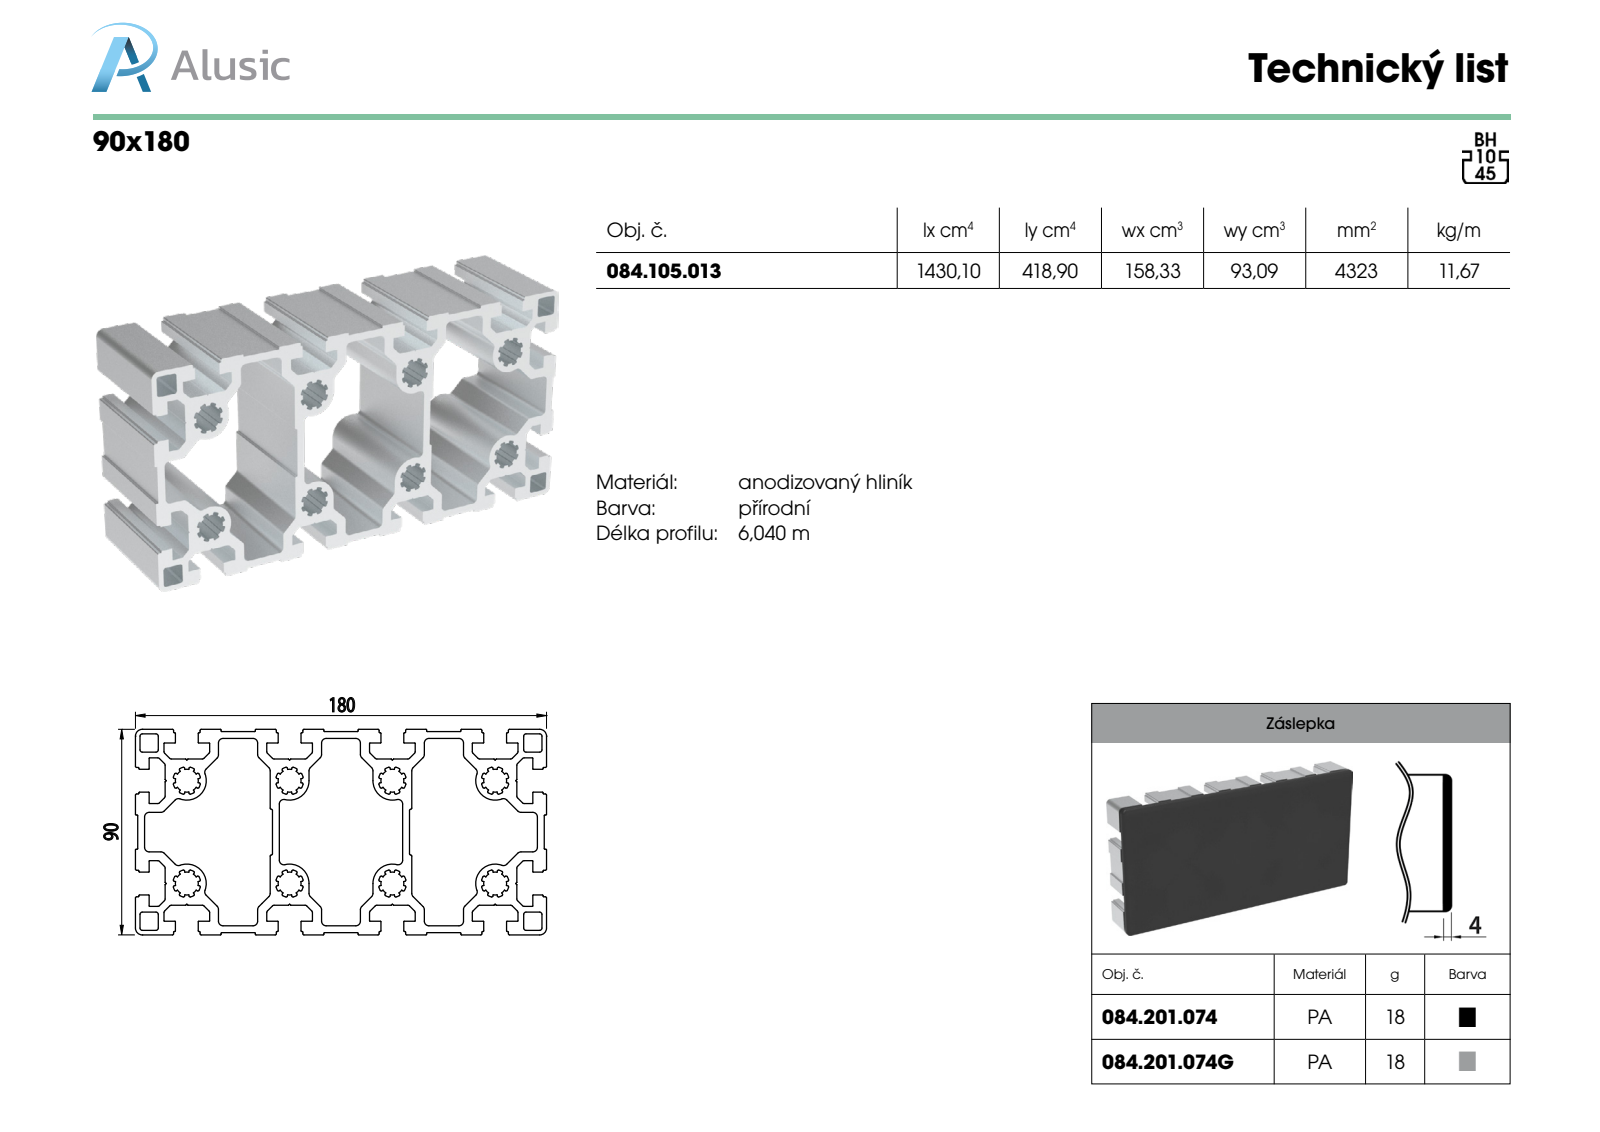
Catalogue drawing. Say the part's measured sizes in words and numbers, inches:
The part is named "084.105.013". Its 3-D file was written by "SolidWorks 2018 (AUTOMOTIVE_DESIGN)". It is 1 solid with 1070 faces: 438 planar, 632 cylindrical and 0 other. Overall it measures 7.087 by 3.937 by 3.543 inches. Its volume is 26.38 cubic inches and its surface area 367.8 square inches. Partial cylindrical surfaces (rounded edges, fillets, slot ends): 160 of radius 0.02, 80 of radius 0.012, 64 of radius 0.039, 52 of radius 0.079, 48 of radius 0.008, 36 of radius 0.004, 8 of radius 0.197, 8 of radius 0.24. The main face-to-face distances are 0.157, 0.039, 0.079, 0.118, 0.236, 0.354, 0.512, 2.323, 0.472, 0.276.
